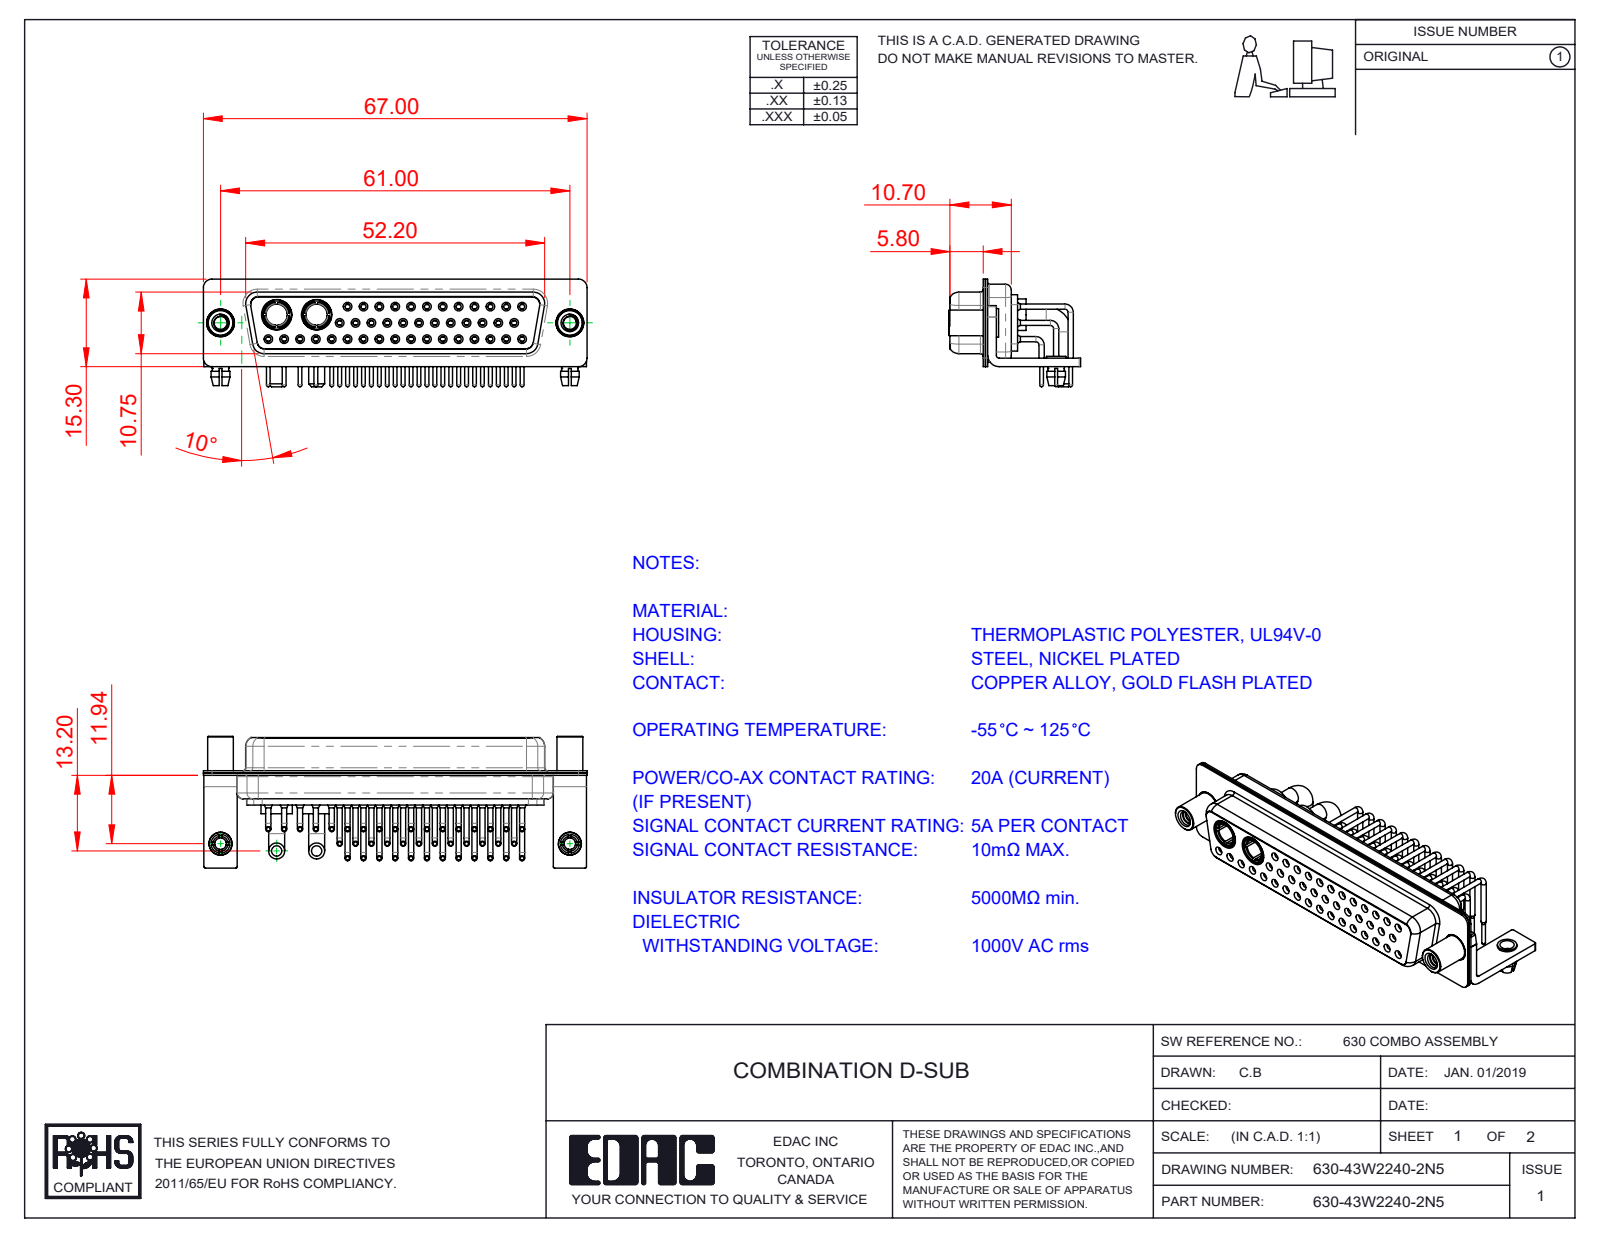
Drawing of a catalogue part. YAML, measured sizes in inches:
part_name: "630Combo Shell Front_50 Contacts; 630Combo Board Lock_50 Contacts; 630-43W2240-2N5; 630Combo Housing_43W2 (+7 more)"
step_written_by: "SolidWorks 2020 (CONFIG_CONTROL_DESIGN)"
units: inches
bodies: {solids: 54, faces: 2788, planar: 810, cylindrical: 1222, other: 756}
overall_size: [2.638, 0.906, 0.74]
volume: 0.472
surface_area: 26.51
round_holes:
  - {diameter: 0.079, count: 43}
  - {diameter: 0.035, count: 41}
  - {diameter: 0.043, count: 41}
  - {diameter: 0.059, count: 41}
  - {diameter: 0.063, count: 29}
  - {diameter: 0.067, count: 12}
  - {diameter: 0.191, count: 4}
  - {diameter: 0.089, count: 2}
  - {diameter: 0.098, count: 2}
  - {diameter: 0.126, count: 2}
  - {diameter: 0.146, count: 2}
  - {diameter: 0.157, count: 2}
round_bosses_or_shafts:
  - {diameter: 0.035, count: 41}
  - {diameter: 0.026, count: 41}
  - {diameter: 0.063, count: 12}
  - {diameter: 0.11, count: 4}
  - {diameter: 0.217, count: 2}
  - {diameter: 0.205, count: 2}
  - {diameter: 0.197, count: 2}
  - {diameter: 0.195, count: 2}
partial_cylinders:
  - {radius: 0.01, count: 16}
  - {radius: 0.059, count: 16}
  - {radius: 0.079, count: 13}
  - {radius: 0.053, count: 12}
  - {radius: 0.063, count: 8}
  - {radius: 0.02, count: 5}
  - {radius: 0.024, count: 4}
  - {radius: 0.026, count: 4}
face_to_face_distances: [0.016, 0.059, 0.236, 0.22, 0.031, 0.228, 0.205, 0.444, 0.072, 0.244]
hole_center_spacings: [0.109, 0.124, 0.218, 0.327, 0.436, 0.545, 0.654, 0.763]
